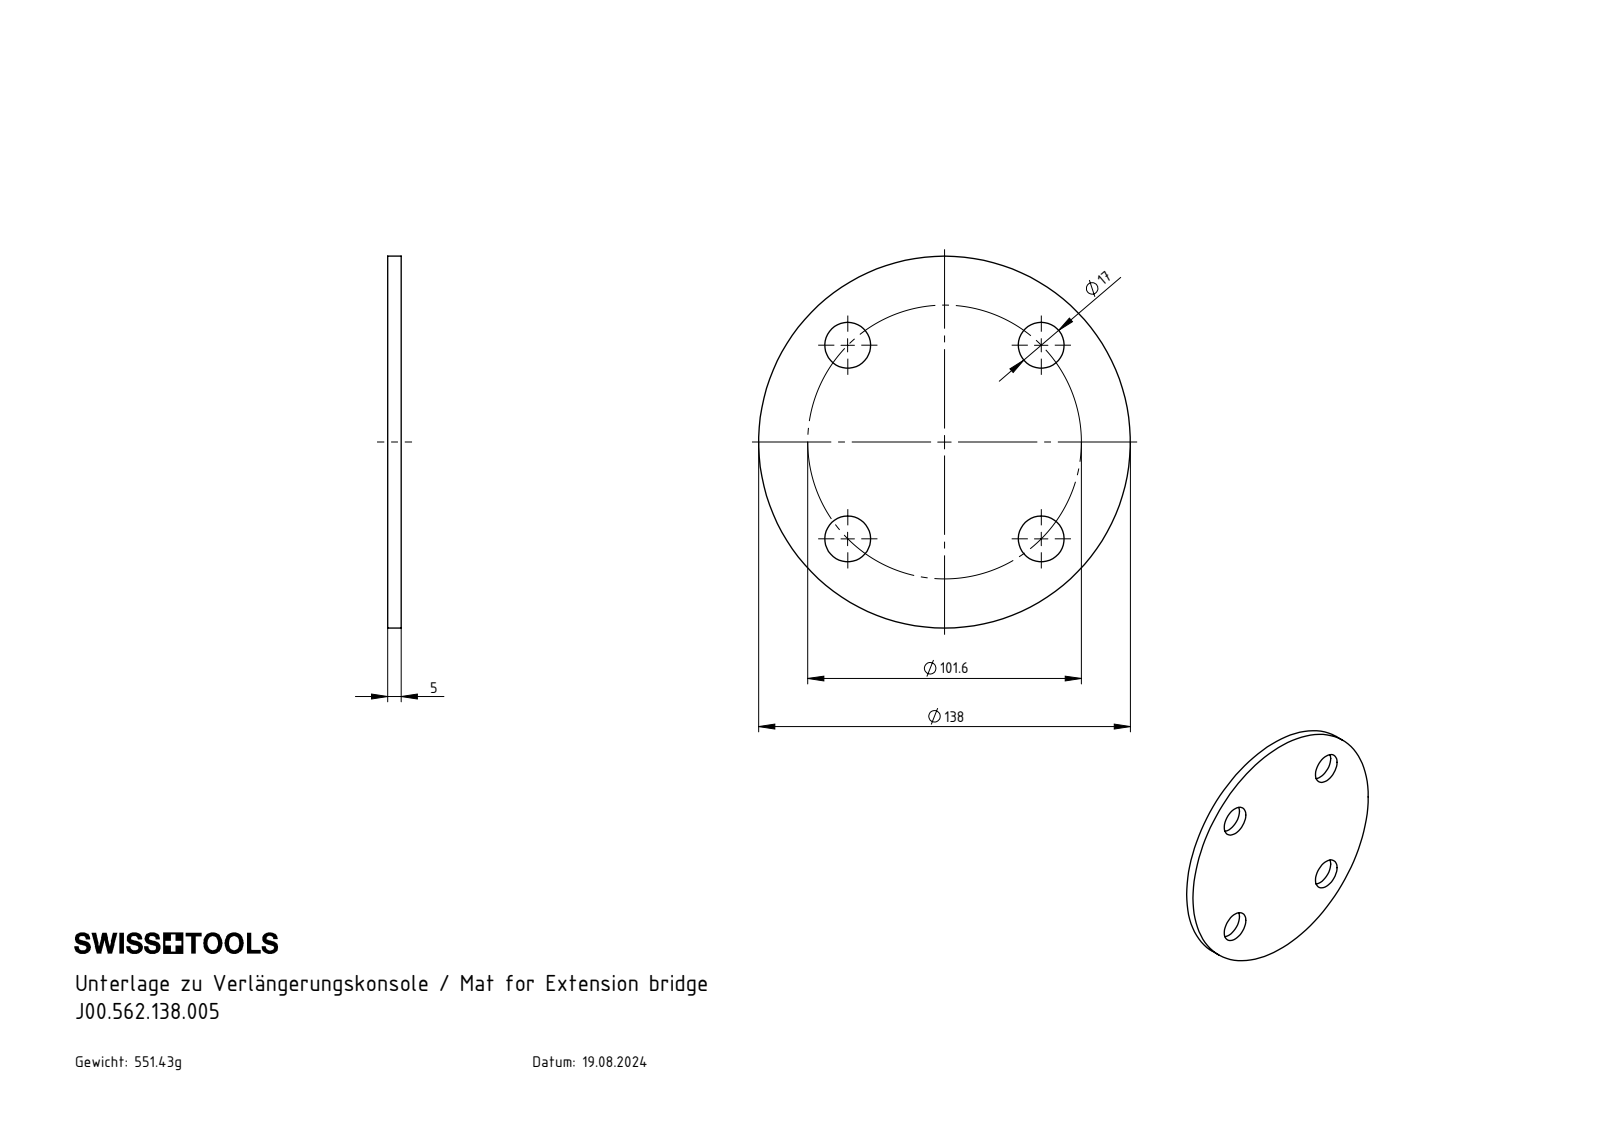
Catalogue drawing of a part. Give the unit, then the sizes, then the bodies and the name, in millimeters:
Units: millimetres
Overall size (bounding box): 138 × 138 × 5
Round holes (diameter × count): ⌀17 ×4
Round bosses / shafts (diameter × count): ⌀138 ×1
Main face-to-face distances: 5
Hole centre spacings: 71.84, 101.6
Volume: 70 246 mm³ · Surface area: 31 334 mm²
Bodies: 1 solid, 12 faces (2 planar, 10 cylindrical, 0 other)
Part name (STEP PRODUCT): J00.562.138.005
STEP written by: SolidWorks 2022 (CONFIG_CONTROL_DESIGN)
